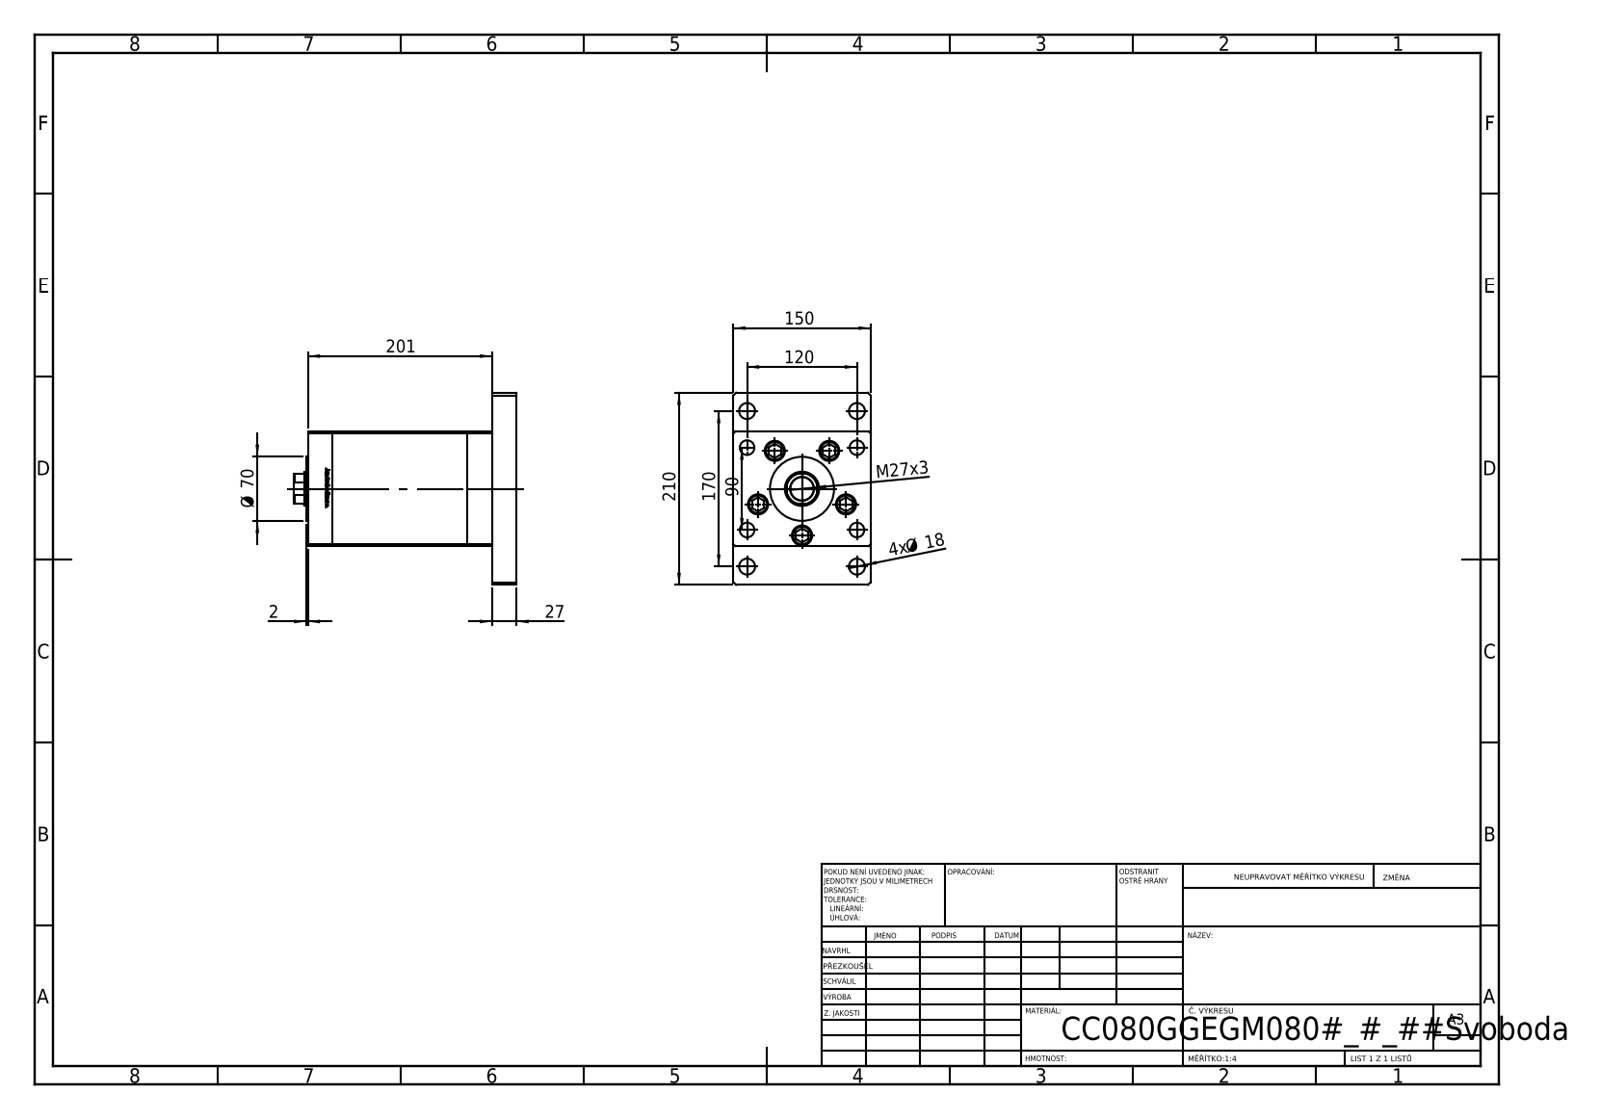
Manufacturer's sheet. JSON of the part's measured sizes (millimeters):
{"part_name": "ALLEN BOLT; V220C_G_MIDDLE; V220C BACK_G; V220C_VC_G (+2 more)", "step_written_by": "SolidWorks 2019 (CONFIG_CONTROL_DESIGN)", "units": "millimeters", "bodies": {"solids": 19, "faces": 1313, "planar": 518, "cylindrical": 189, "other": 606}, "overall_size": [243, 210, 150], "volume_mm3": 4045000, "surface_area_mm2": 449237, "round_holes": [[16, 9], [17.5, 9], [22, 5], [21, 4], [2, 2], [13.16, 2], [25.5, 1], [36, 1], [37.5, 1], [102, 1]], "round_bosses_or_shafts": [[8, 9], [21, 5], [80, 1], [70, 1]], "partial_cylinders_radius": [[0.93, 2], [17.5, 1]], "face_to_face_distances": [27, 174, 201, 150, 147, 125, 54, 167.5, 2, 228], "hole_center_spacings": [51, 40, 75, 104.04, 120, 126.49, 130, 176.92]}
